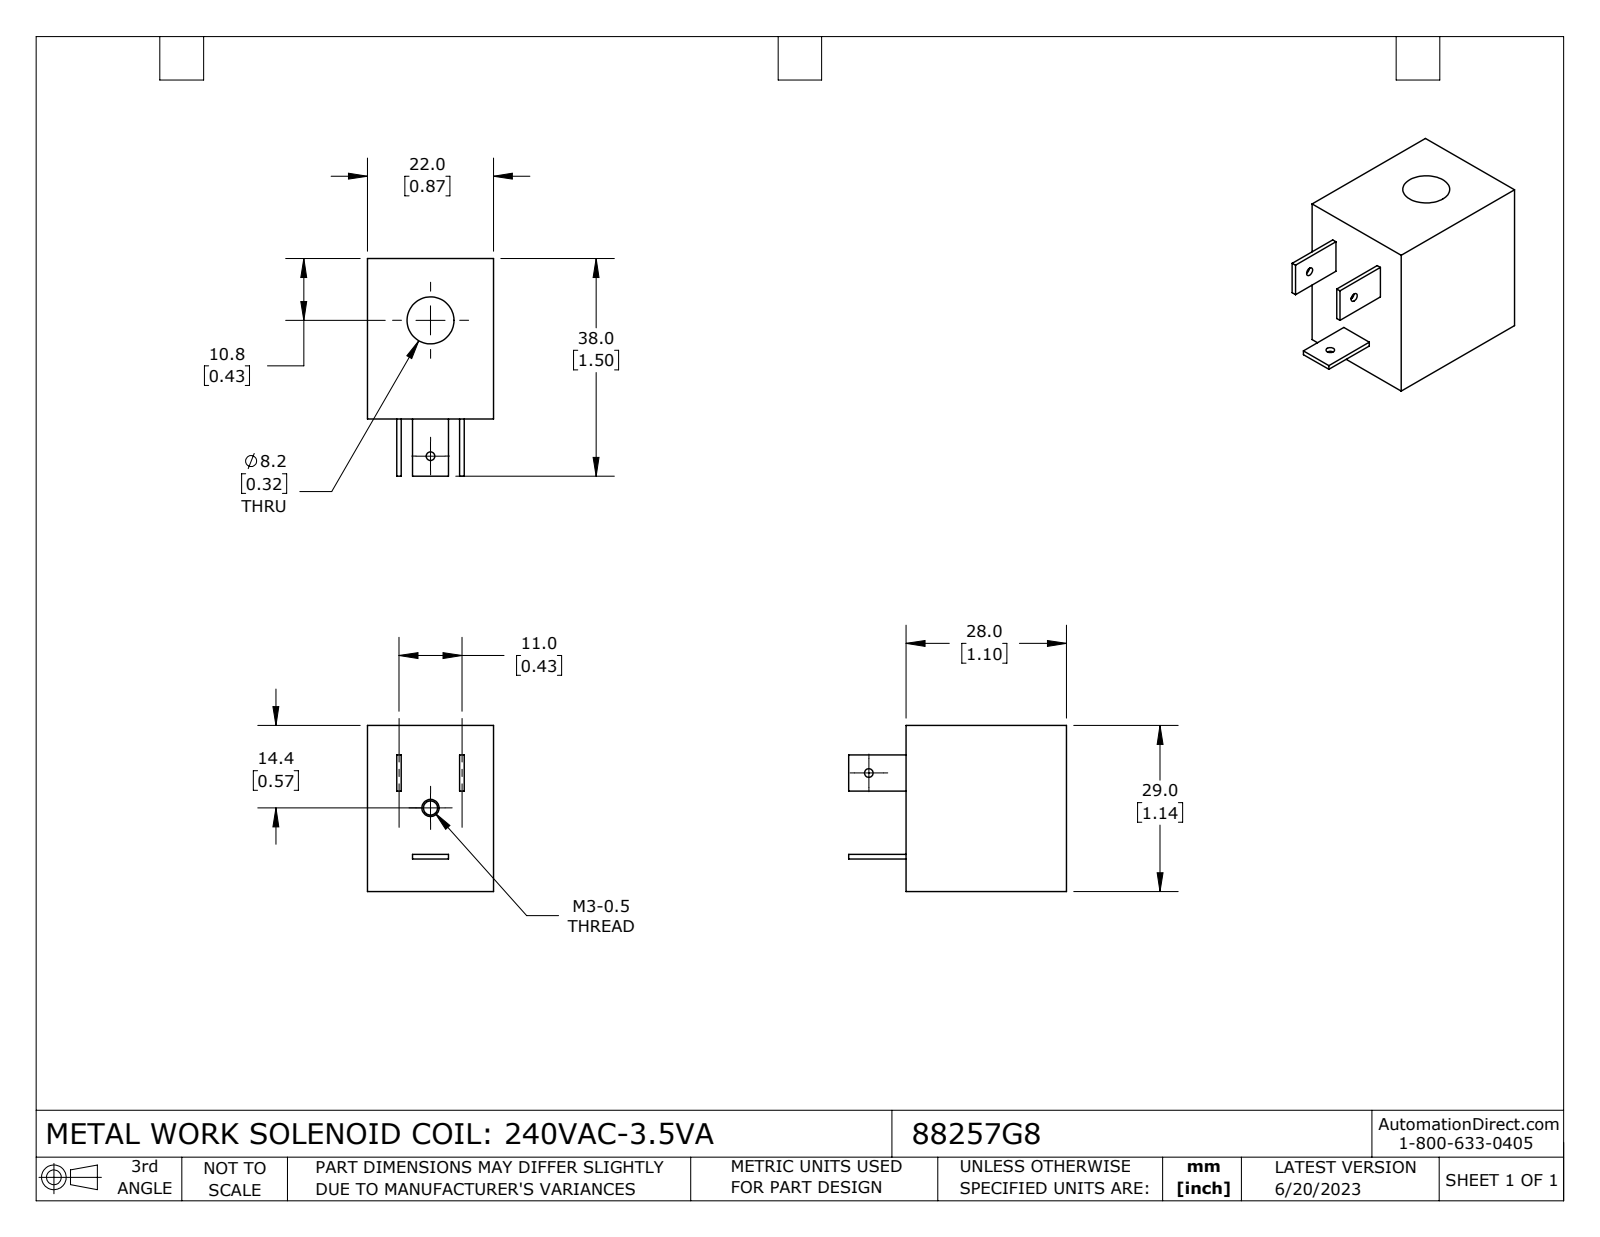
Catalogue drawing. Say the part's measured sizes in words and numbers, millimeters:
The part is named "88257G8". Its 3-D file was written by "SolidWorks 2021 (CONFIG_CONTROL_DESIGN)". It is 1 solid with 35 faces: 21 planar, 10 cylindrical and 4 other. Overall it measures 38 by 29 by 22 millimeters. Its volume is 16 450 cubic millimeters and its surface area 5 239 square millimeters. Round holes: 2 of diameter 1.5, 1 of diameter 2.5, 1 of diameter 8.2. The main face-to-face distances are 22, 28, 29, 0.8, 5.1, 5.9, 16.1, 16.9, 11, 11.8. The hole center spacings are 23.7.
